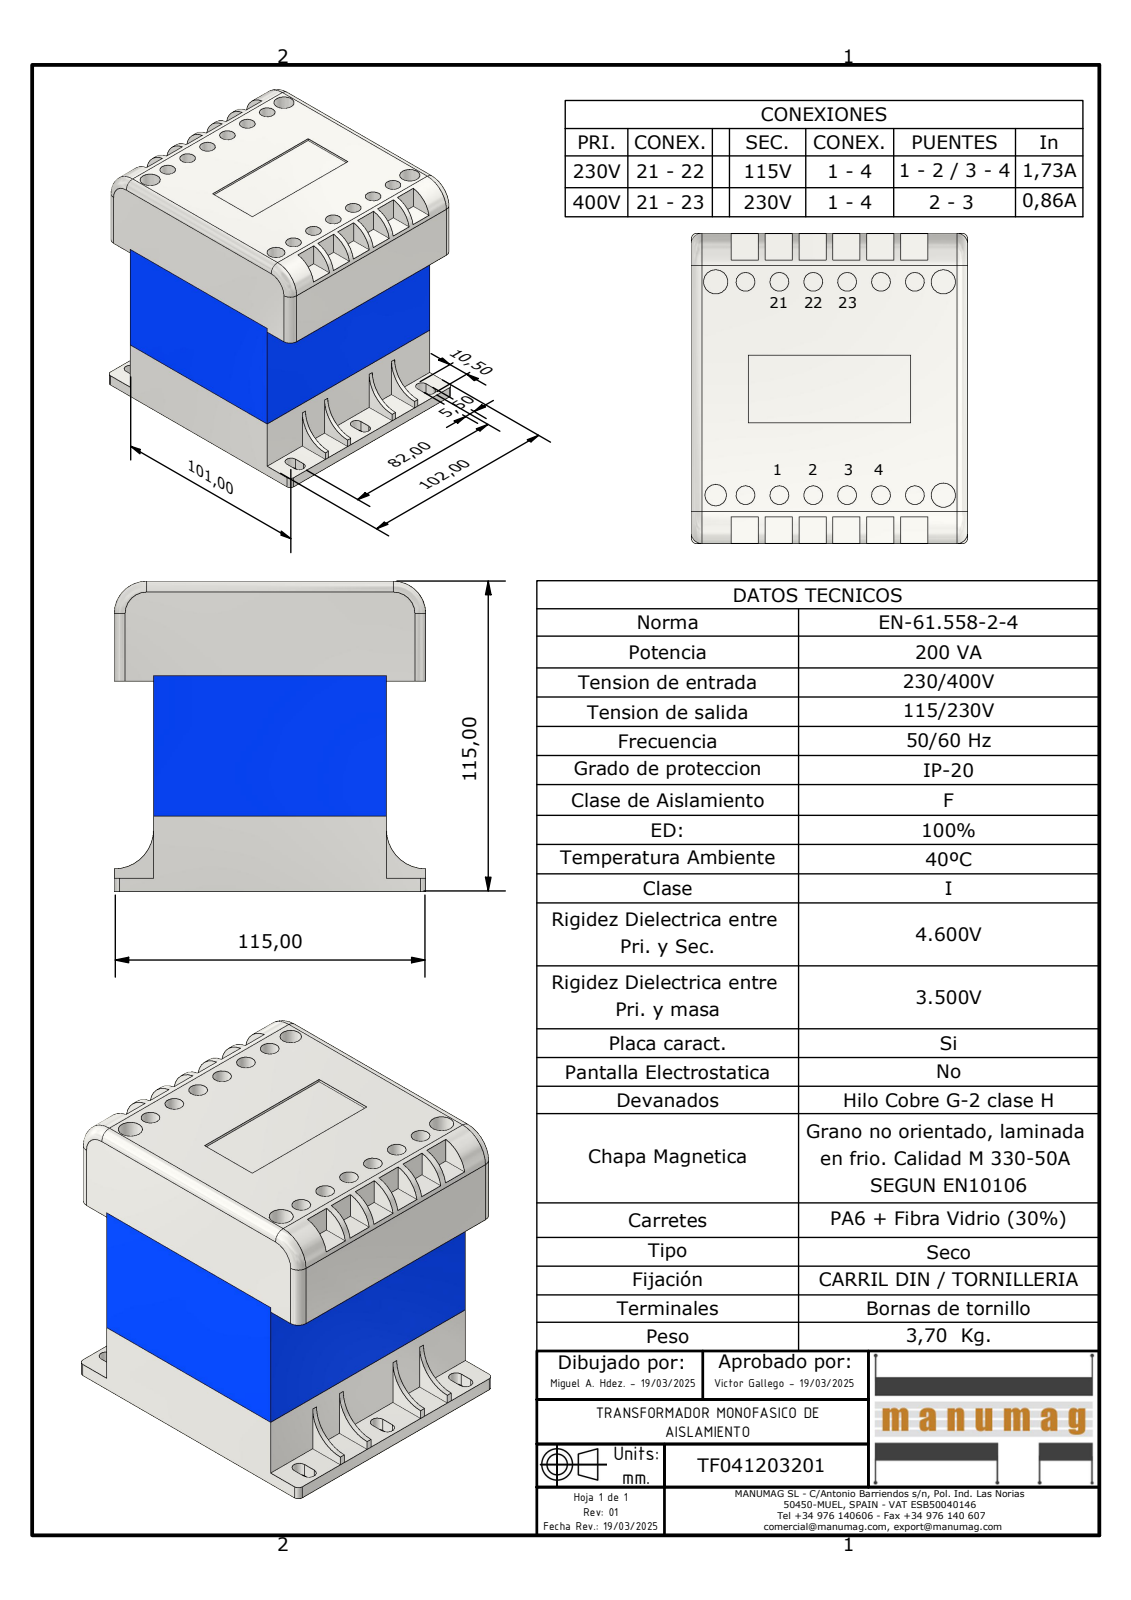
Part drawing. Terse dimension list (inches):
name: TF041203201; INFERIOR EI96; CENTRAL EI96-50; SUPERIOR EI96
written by: Autodesk Inventor 2023 (AUTOMOTIVE_DESIGN)
unit: in
bodies: 11 solids, 200 faces (152 planar, 44 cylindrical, 4 other)
size: 4.528 × 4.528 × 4.016
volume: 29.25 in³; area: 199.5 in²
holes: 12× ⌀0.276, 3× ⌀0.354, 1× ⌀0.315
rounds: 8× R0.098, 6× R0.157, 4× R0.079, 2× R0.472, 2× R0.571
face distances: 0.039, 3.346, 3.976, 0.197, 4.016, 3.15, 4.528, 2.953, 3.386, 3.937
hole spacings: 0.492, 3.149, 0.984, 3.11, 3.262, 1.476, 3.443, 1.969
